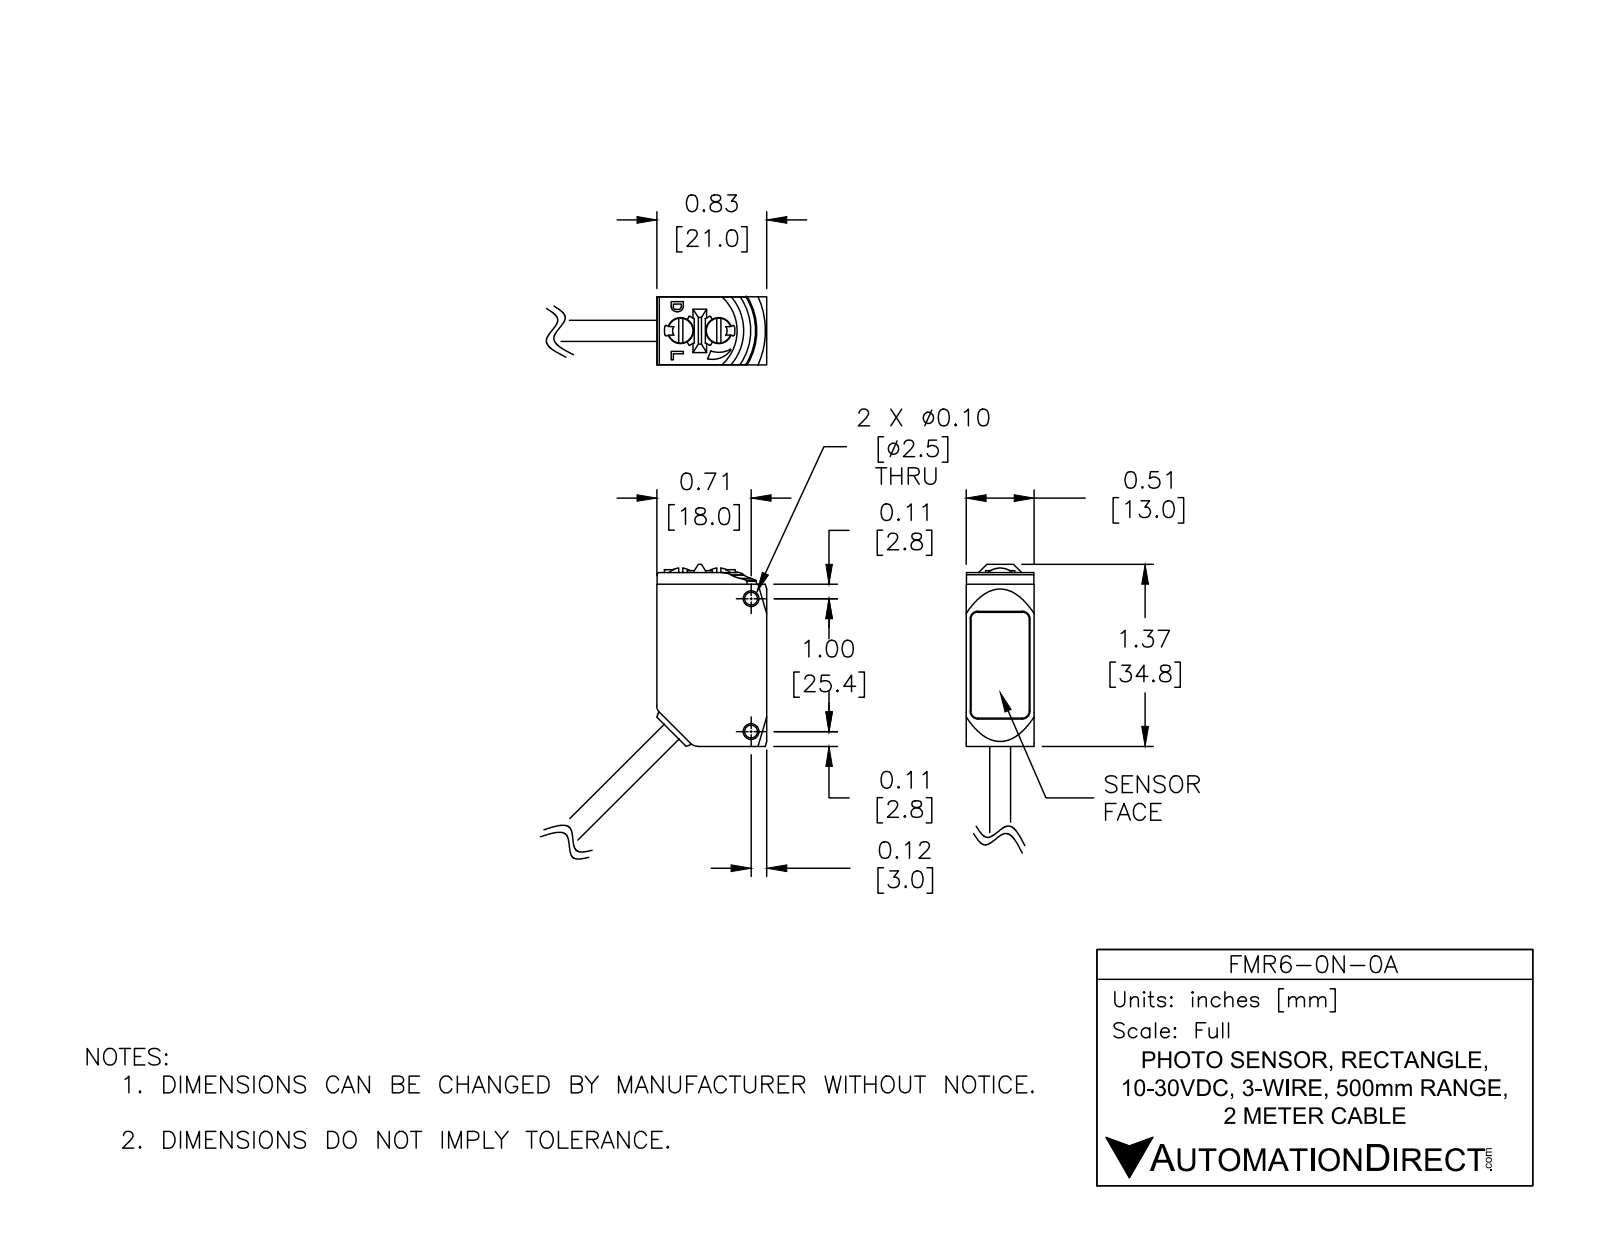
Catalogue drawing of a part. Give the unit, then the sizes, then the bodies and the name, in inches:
Units: inches
Overall size (bounding box): 2.084 × 1.541 × 0.512
Round holes (diameter × count): ⌀0.097 ×2, ⌀0.197 ×2
Round bosses / shafts (diameter × count): ⌀0.189 ×2, ⌀0.157 ×1
Partial cylindrical surfaces — rounded edges, fillets, slot ends (radius × count): R0.018 ×7, R0.02 ×7, R0.008 ×4, R0.01 ×4, R0.051 ×4, R0.059 ×4, R0.004 ×3, R0.018 ×2
Main face-to-face distances: 0.512, 0.827, 1.307, 0.035, 0.51, 0.031, 0.48, 0.037, 0.474, 0.472
Hole centre spacings: 0.287, 1
Volume: 0.542 in³ · Surface area: 5.476 in²
Bodies: 1 solid, 186 faces (89 planar, 72 cylindrical, 25 other)
Part name (STEP PRODUCT): FMR6-0N-0A
STEP written by: SolidWorks 2017 (AUTOMOTIVE_DESIGN)
